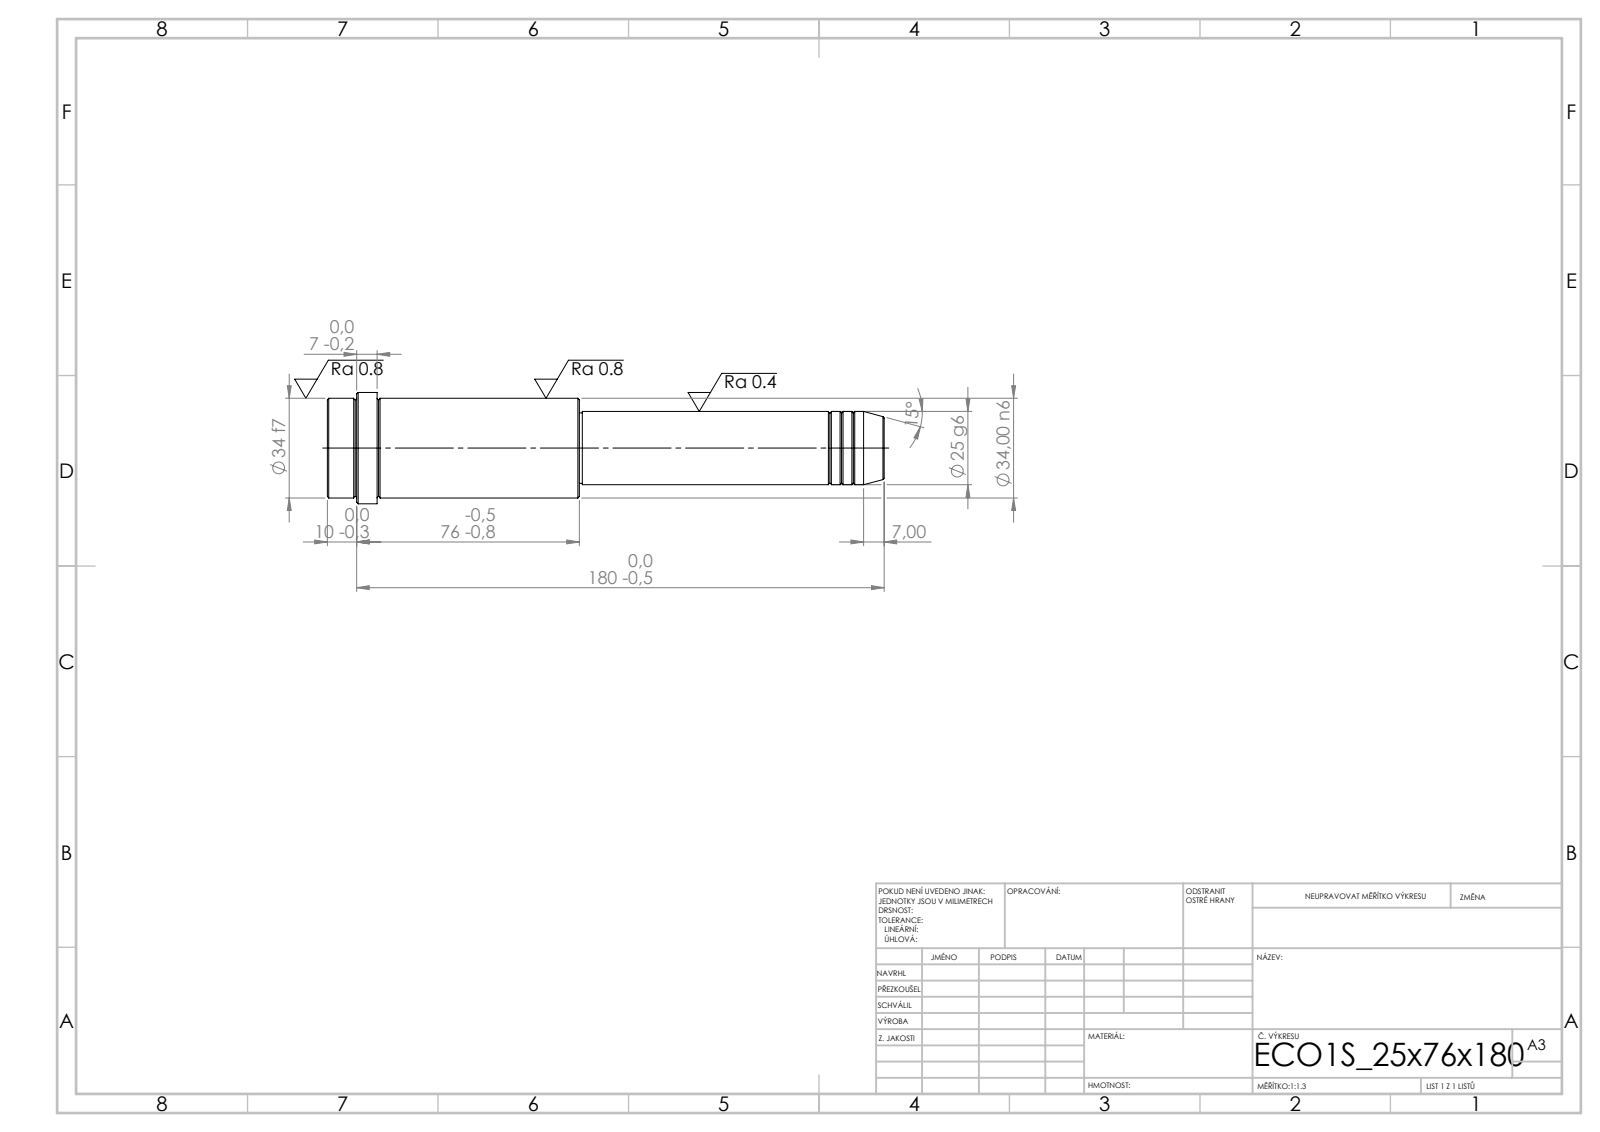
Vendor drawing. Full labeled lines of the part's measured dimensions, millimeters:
STEP written by: SolidWorks 2019 (CONFIG_CONTROL_DESIGN)
Units: millimetres
Bodies: 1 solid, 52 faces (6 planar, 16 cylindrical, 30 other)
Overall size (bounding box): 190 × 38 × 38
Volume: 129 970 mm³ · Surface area: 19 759 mm²
Round bosses / shafts (diameter × count): ⌀38 ×1, ⌀34 ×1, ⌀25 ×1, ⌀24 ×1
Main face-to-face distances: 86, 104, 190, 173, 69, 17, 180, 76, 7, 10
